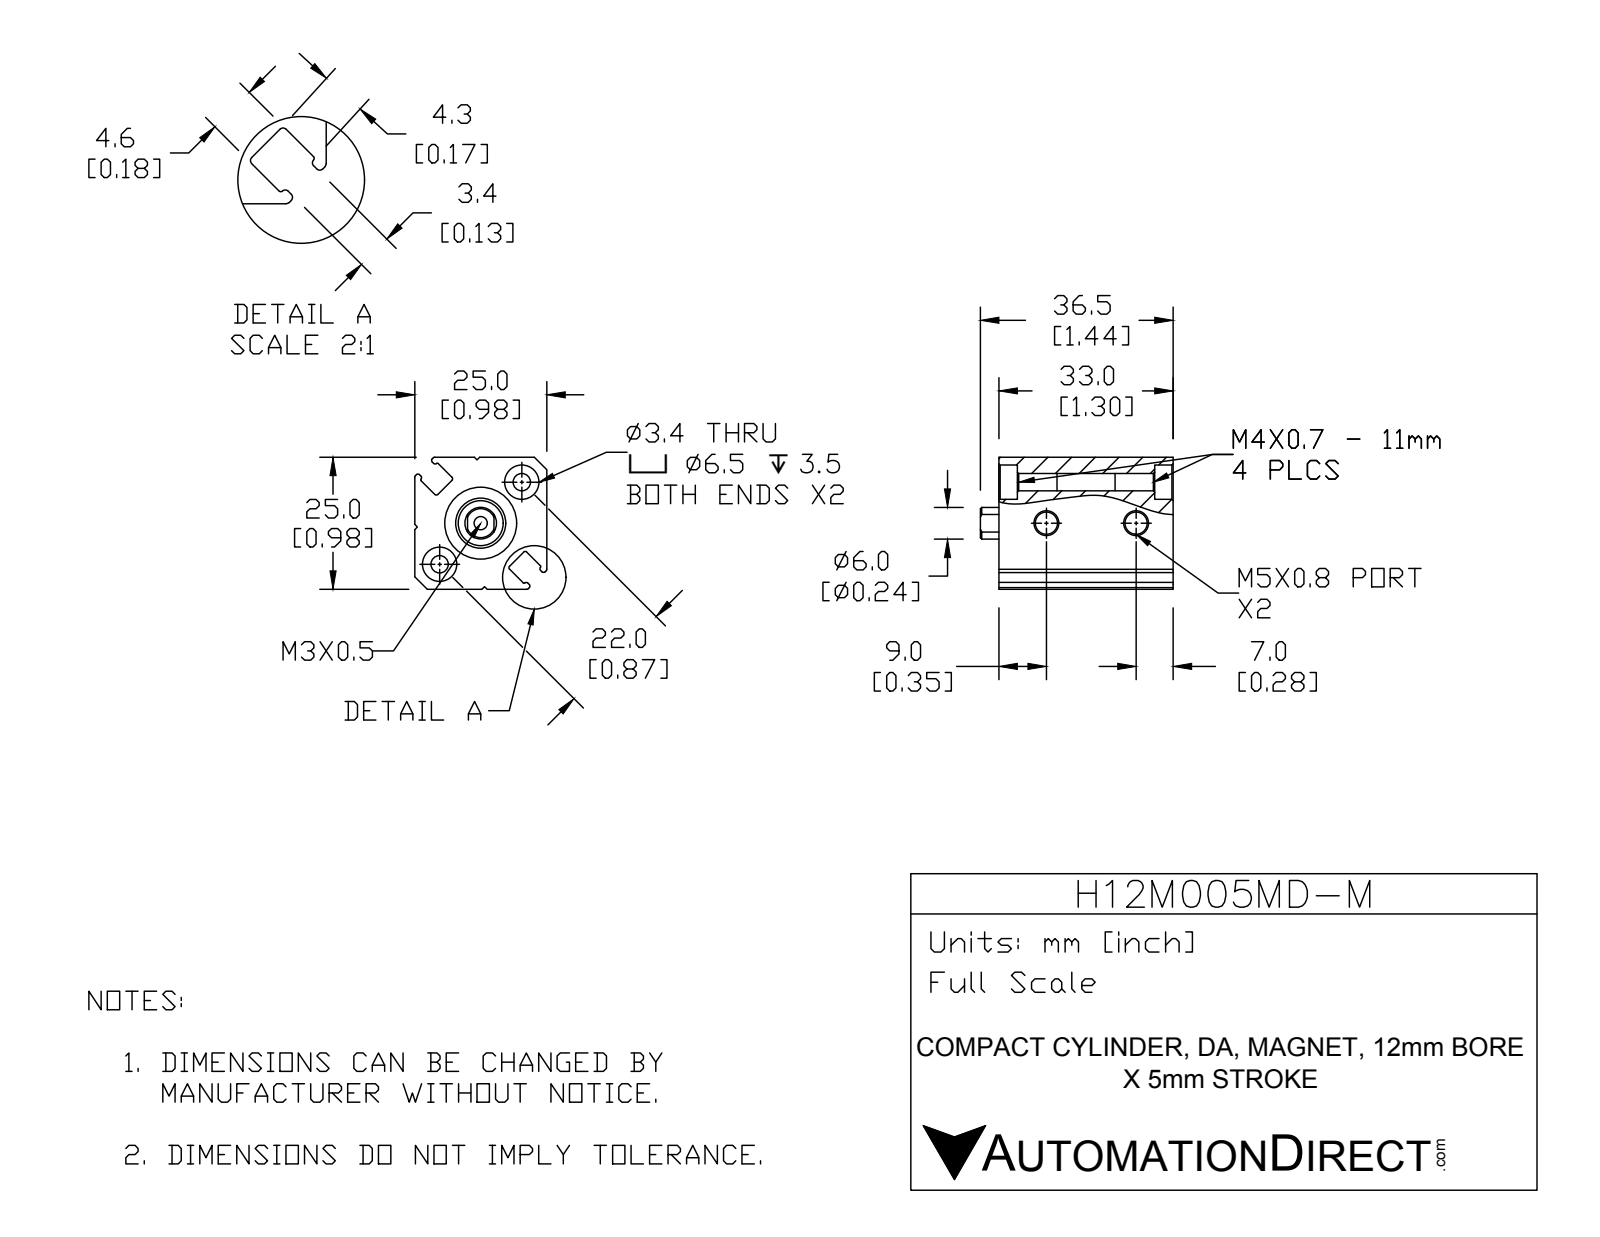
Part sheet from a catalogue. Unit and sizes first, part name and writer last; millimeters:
Units: millimetres
Overall size (bounding box): 36.5 × 25 × 25
Round holes (diameter × count): ⌀3.3 ×2, ⌀4.2 ×2, ⌀6.5 ×2, ⌀2.5 ×1, ⌀6 ×1, ⌀12 ×1, ⌀13.6 ×1
Round bosses / shafts (diameter × count): ⌀9.5 ×1
Partial cylindrical surfaces — rounded edges, fillets, slot ends (radius × count): R0.4 ×16, R0.2 ×4
Main face-to-face distances: 25, 33, 5.5, 4.6, 18.3, 27.5, 13.7, 12.7, 24, 19.2
Hole centre spacings: 11, 17, 22.01
Volume: 16 725 mm³ · Surface area: 8 203 mm²
Bodies: 2 solids, 128 faces (49 planar, 54 cylindrical, 25 other)
Part name (STEP PRODUCT): H12M005MD-M-BODY; H12M005MD-M-PISTON; H12M005MD-M
STEP written by: SolidWorks 2015 (CONFIG_CONTROL_DESIGN)
